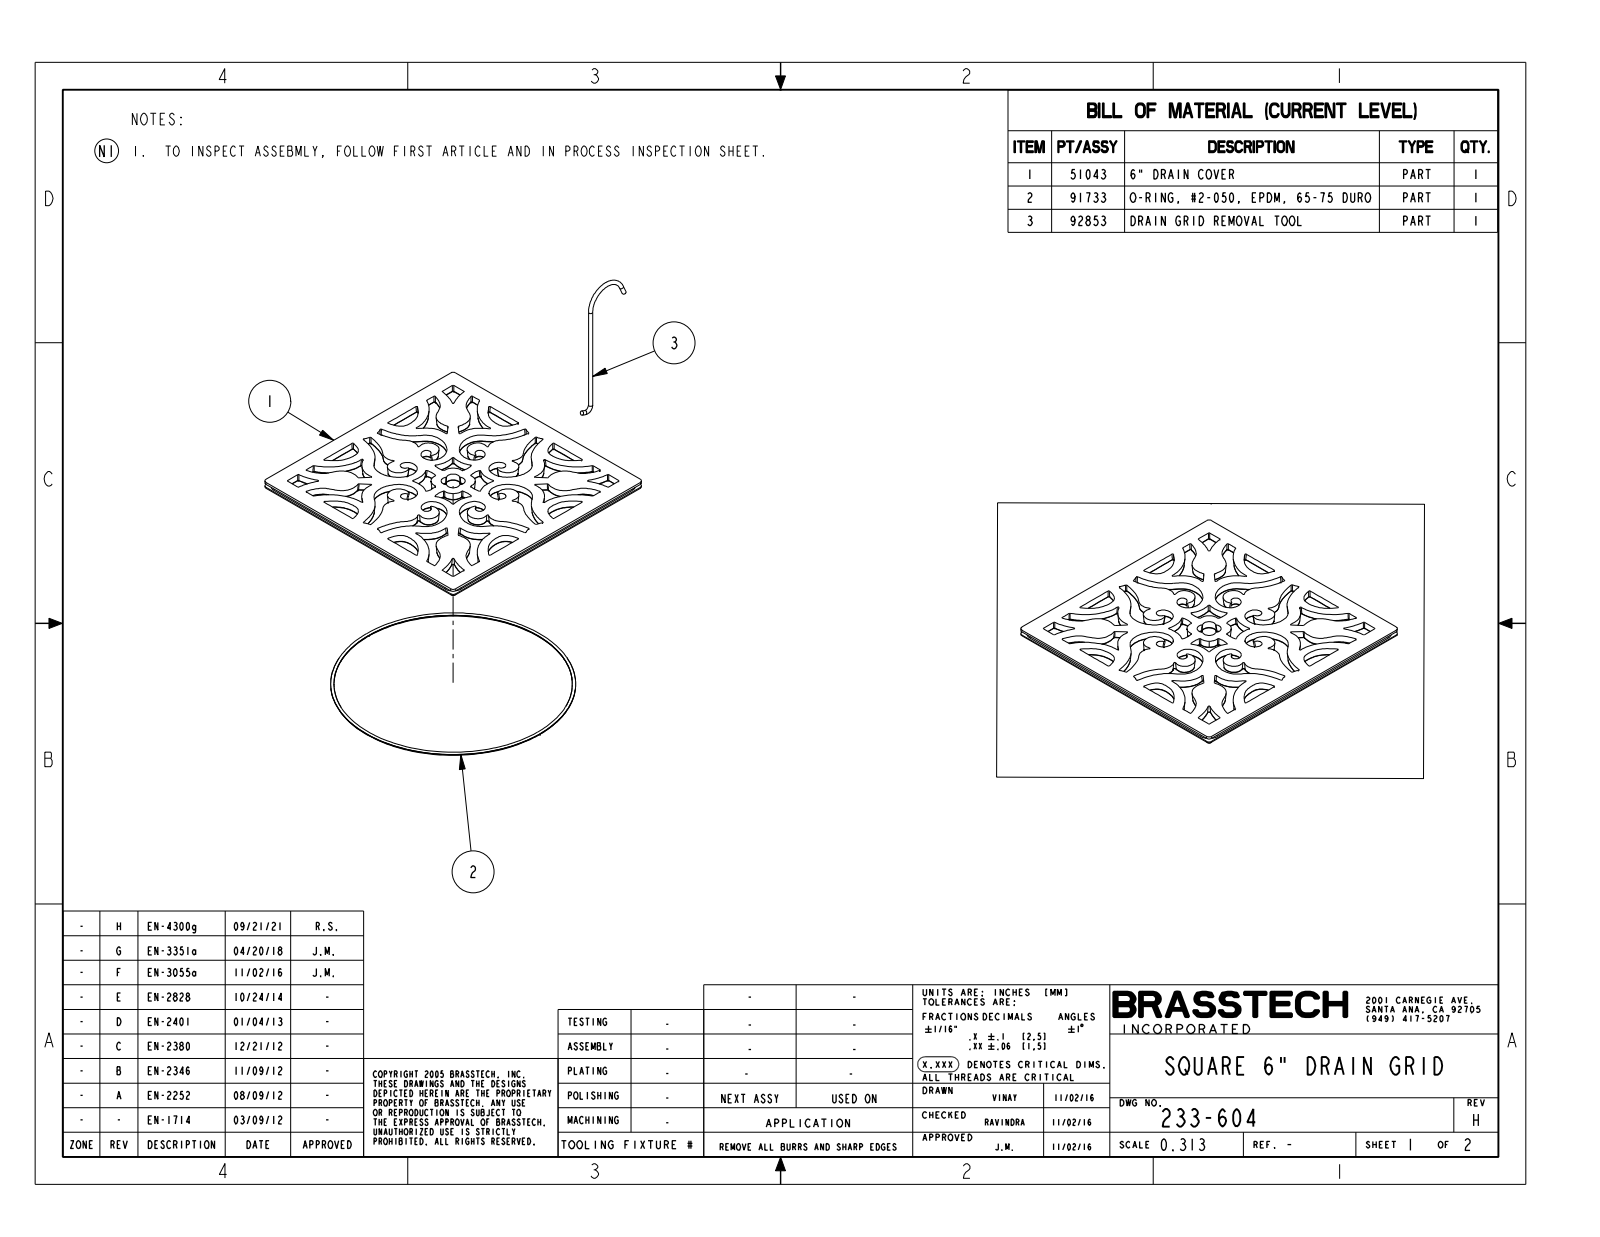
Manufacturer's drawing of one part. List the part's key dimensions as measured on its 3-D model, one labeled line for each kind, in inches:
Part name (STEP PRODUCT): 51043
STEP written by: CREO PARAMETRIC BY PTC INC, 2018400 (AUTOMOTIVE_DESIGN)
Units: inches
Bodies: 1 solid, 556 faces (36 planar, 32 cylindrical, 488 other)
Overall size (bounding box): 5.895 × 5.895 × 0.188
Volume: 4.232 in³ · Surface area: 72.05 in²
Partial cylindrical surfaces — rounded edges, fillets, slot ends (radius × count): R0.02 ×16, R0.08 ×4, R0.25 ×4
Main face-to-face distances: 0.188, 0.042, 5.854, 0.054, 0.134, 0.134, 0.08, 0.054, 5.895, 5.812
